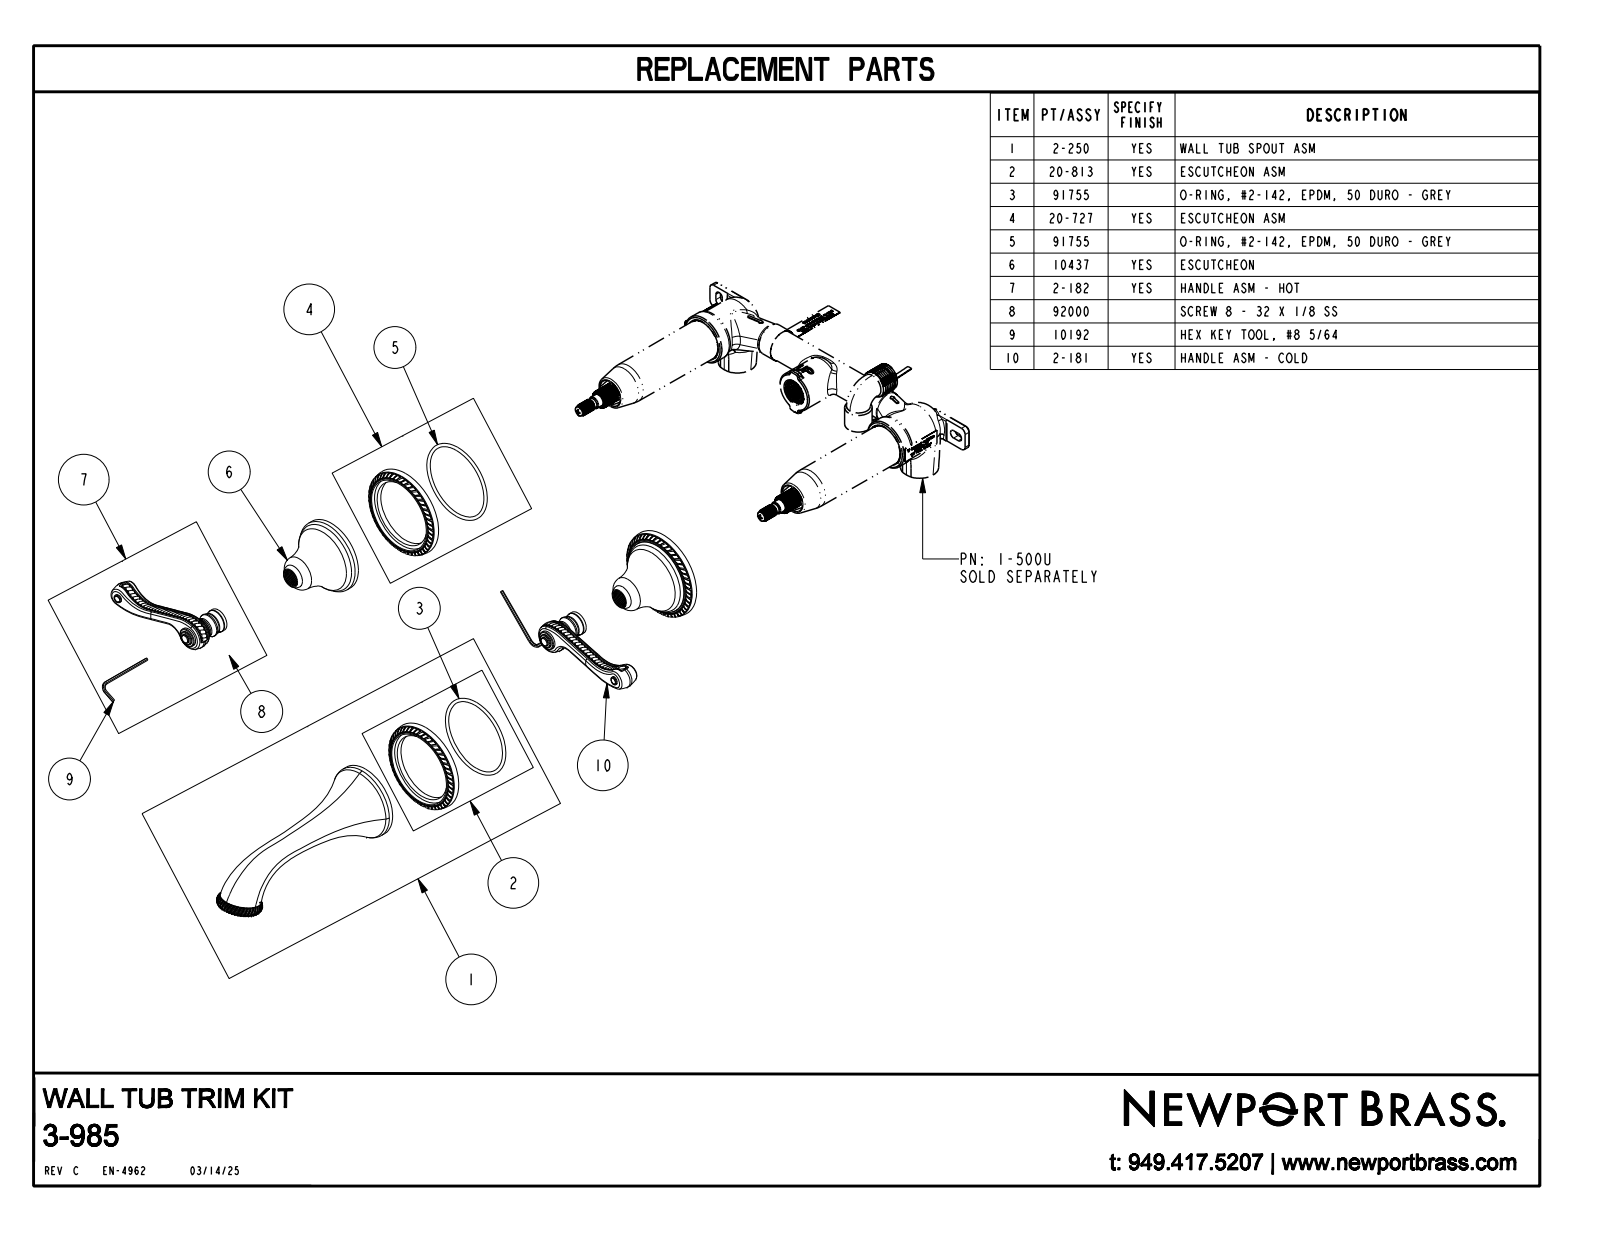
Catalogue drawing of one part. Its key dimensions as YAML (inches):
part_name: "3-985_SW0002"
step_written_by: "CREO PARAMETRIC BY PTC INC, 2018400 (AUTOMOTIVE_DESIGN)"
units: inches
bodies: {solids: 3, faces: 1960, planar: 376, cylindrical: 436, other: 1148}
overall_size: [14.57, 8.845, 6.295]
volume: 20.27
surface_area: 93.17
round_holes:
  - {diameter: 0.13, count: 2}
round_bosses_or_shafts:
  - {diameter: 0.26, count: 4}
  - {diameter: 2.35, count: 2}
  - {diameter: 0.73, count: 2}
  - {diameter: 0.7, count: 2}
  - {diameter: 0.6, count: 2}
  - {diameter: 0.44, count: 2}
  - {diameter: 0.29, count: 2}
  - {diameter: 2.345, count: 1}
partial_cylinders:
  - {radius: 0.15, count: 147}
  - {radius: 0.09, count: 75}
  - {radius: 0.12, count: 72}
  - {radius: 0.224, count: 40}
  - {radius: 11, count: 4}
  - {radius: 0.121, count: 3}
  - {radius: 0.137, count: 3}
face_to_face_distances: [3.24, 3.23, 2.75, 2.74, 0.49, 0.3, 0.29, 2.45, 2.94, 1.95]
